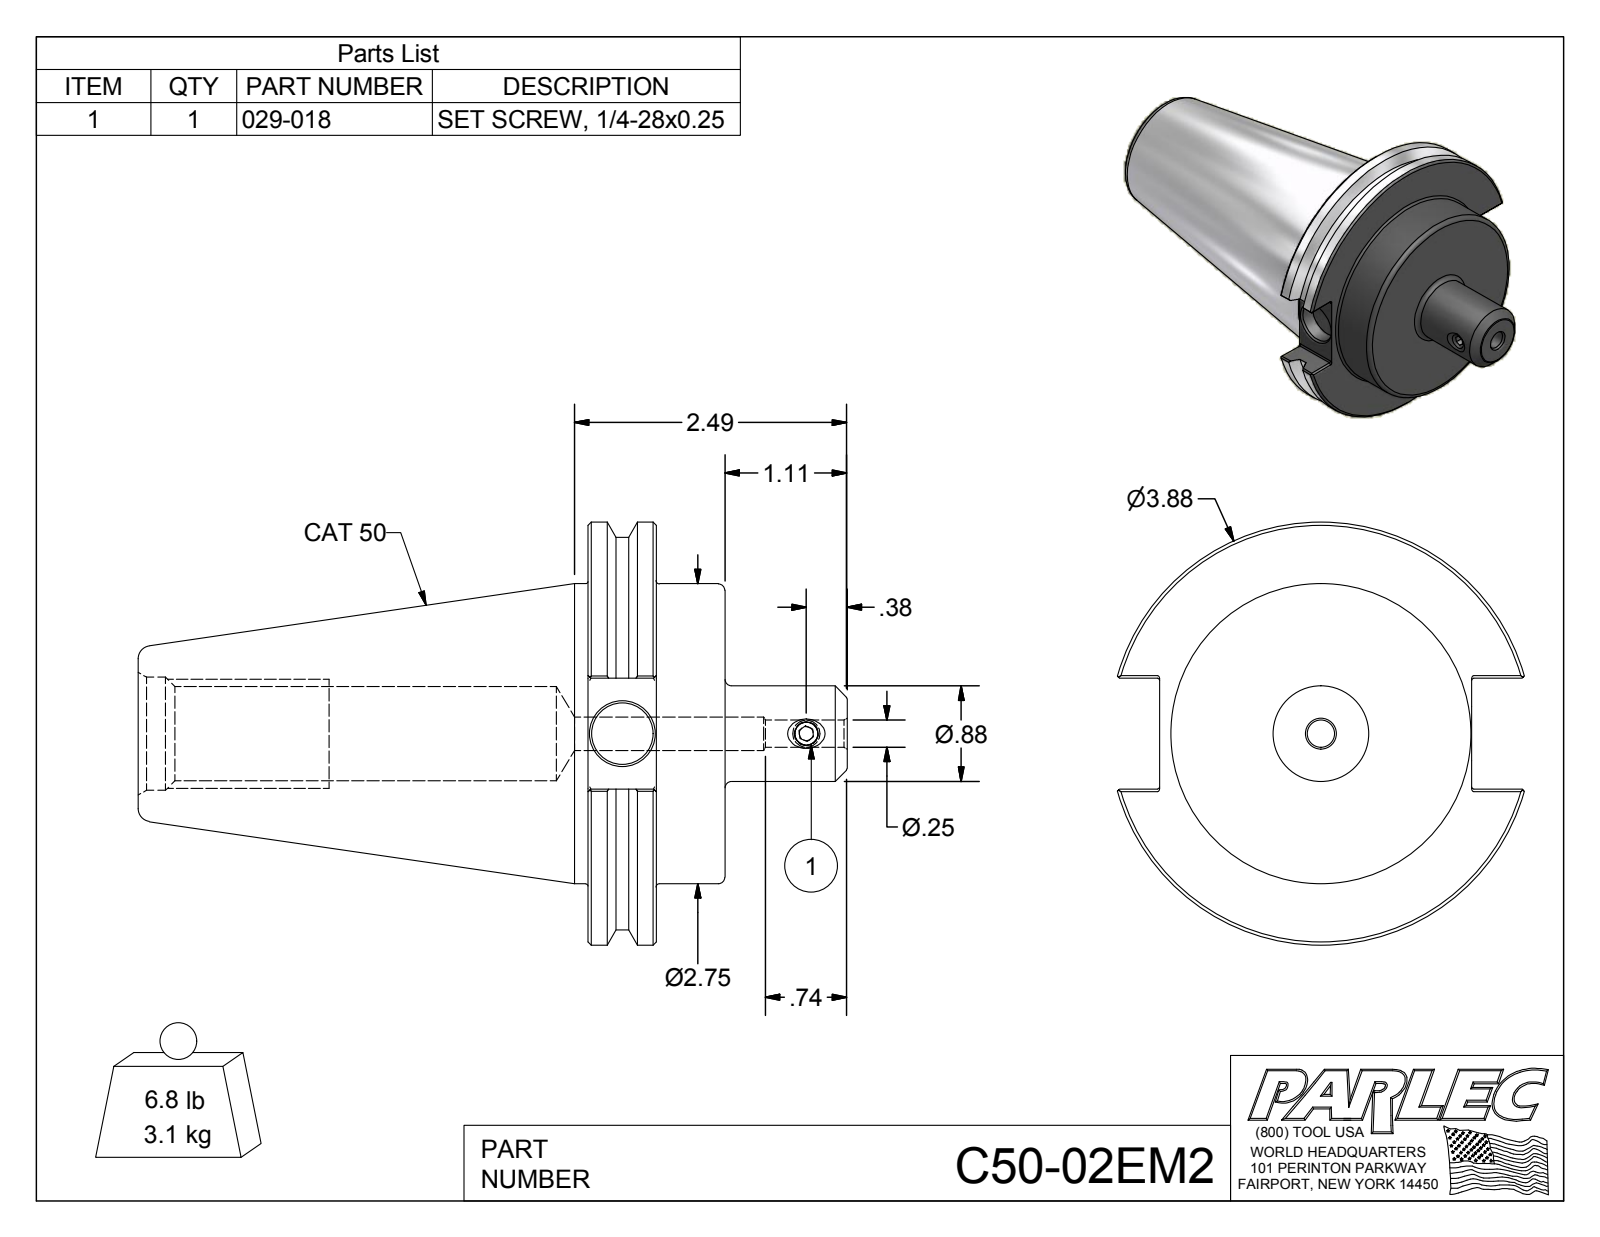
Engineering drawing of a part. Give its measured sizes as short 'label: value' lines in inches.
name: C50-02EM2; C50-02EM2-1; 029-018
written by: Autodesk Inventor 2012 (AUTOMOTIVE_DESIGN)
unit: in
bodies: 2 solids, 107 faces (41 planar, 30 cylindrical, 36 other)
size: 6.5 × 3.875 × 3.729
volume: 24.08 in³; area: 77.41 in²
holes: 1× ⌀0.209, 1× ⌀0.211, 1× ⌀0.25, 1× ⌀0.307, 1× ⌀0.315, 1× ⌀0.399, 1× ⌀0.865, 1× ⌀1.038
bosses: 1× ⌀3.875, 1× ⌀3.594, 1× ⌀2.75, 1× ⌀2.73, 1× ⌀0.875, 1× ⌀0.25
rounds: 12× R0.02
face distances: 1.255, 0.625, 0.63, 4.125, 4.75, 5.38, 2.86, 1.015, 4.363, 0.238
hole spacings: 1.685
